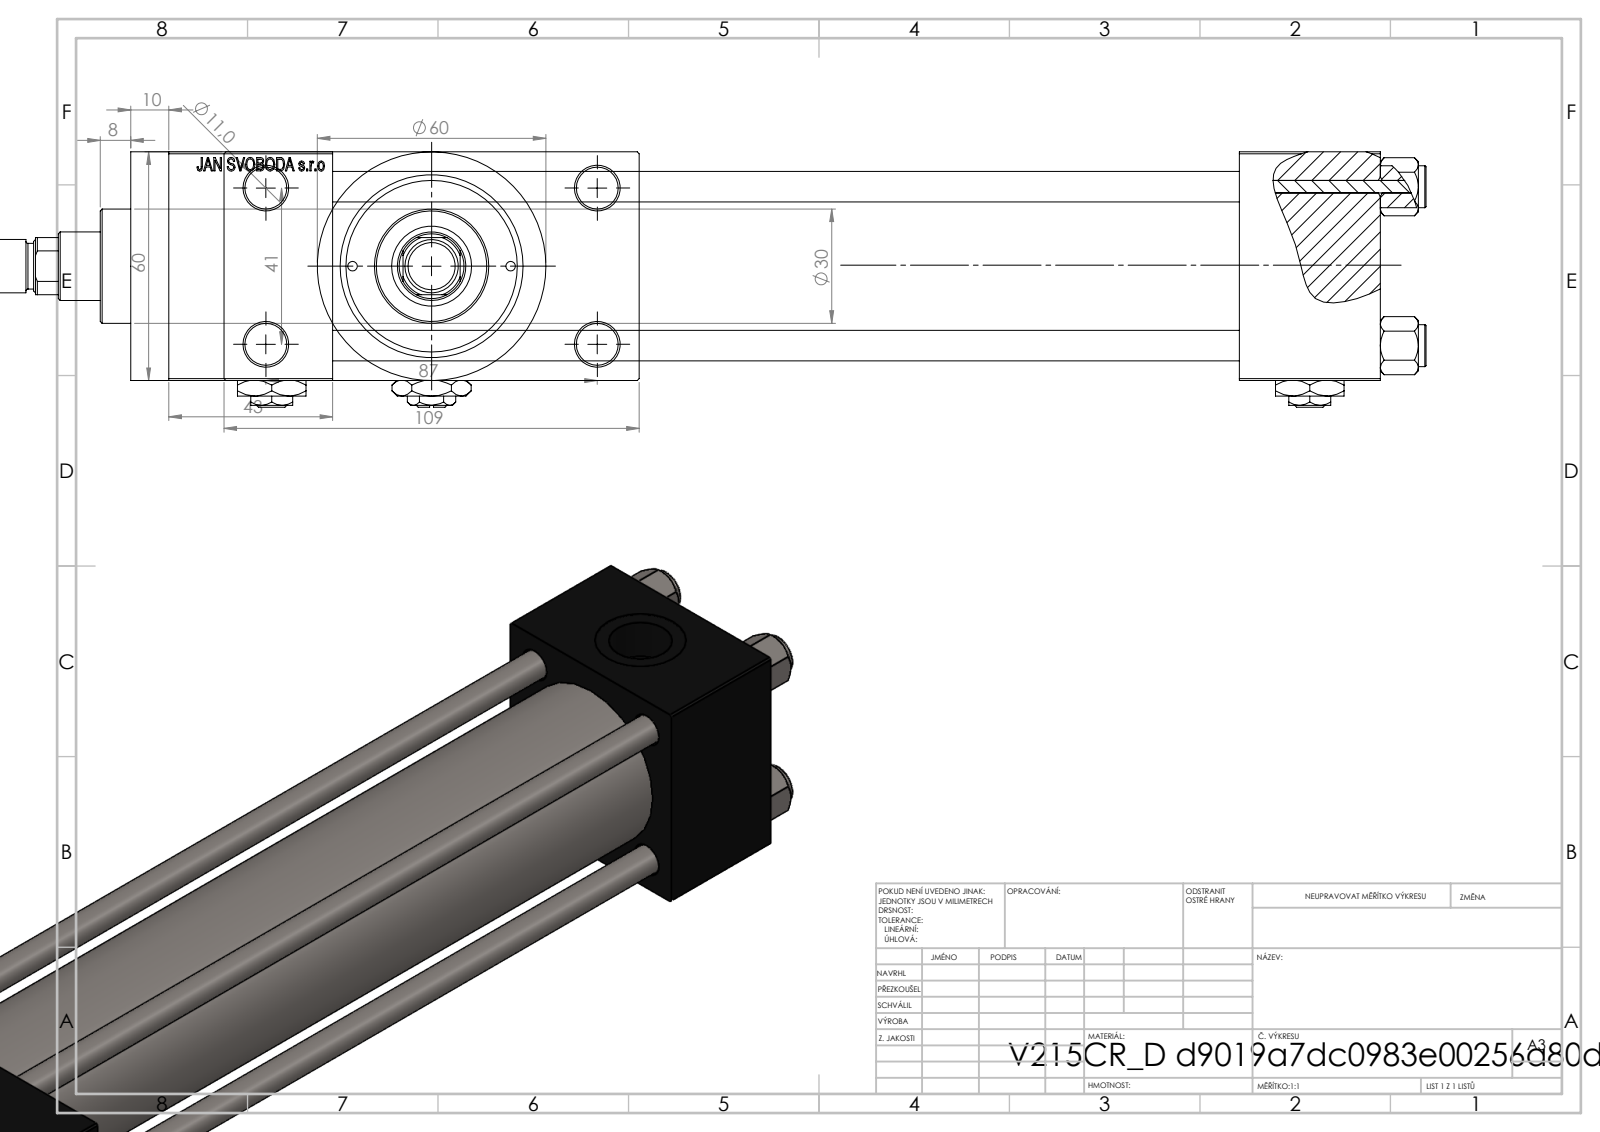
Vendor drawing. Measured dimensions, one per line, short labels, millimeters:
name: V215_VC_A; V215CR_D_TYCINKA; V215CR_D_Body; ROD_END_AH (+3 more)
written by: SolidWorks 2019 (CONFIG_CONTROL_DESIGN)
unit: mm
bodies: 14 solids, 1228 faces (552 planar, 108 cylindrical, 568 other)
size: 383 × 109 × 67
volume: 672 996 mm³; area: 201 905 mm²
holes: 4× ⌀8, 4× ⌀11, 2× ⌀2.5, 2× ⌀7, 2× ⌀16.66, 2× ⌀24, 1× ⌀8.5, 1× ⌀18, 1× ⌀21, 1× ⌀31, 1× ⌀40, 1× ⌀45
bosses: 4× ⌀11, 1× ⌀60, 1× ⌀46, 1× ⌀30, 1× ⌀14, 1× ⌀12
rounds: 1× R8.5
face distances: 60, 24.5, 84.5, 238, 37, 275, 43, 318, 281, 109
hole spacings: 20.85, 22.65, 29.49, 30.62, 41.7, 46.53, 47.15, 48.09
